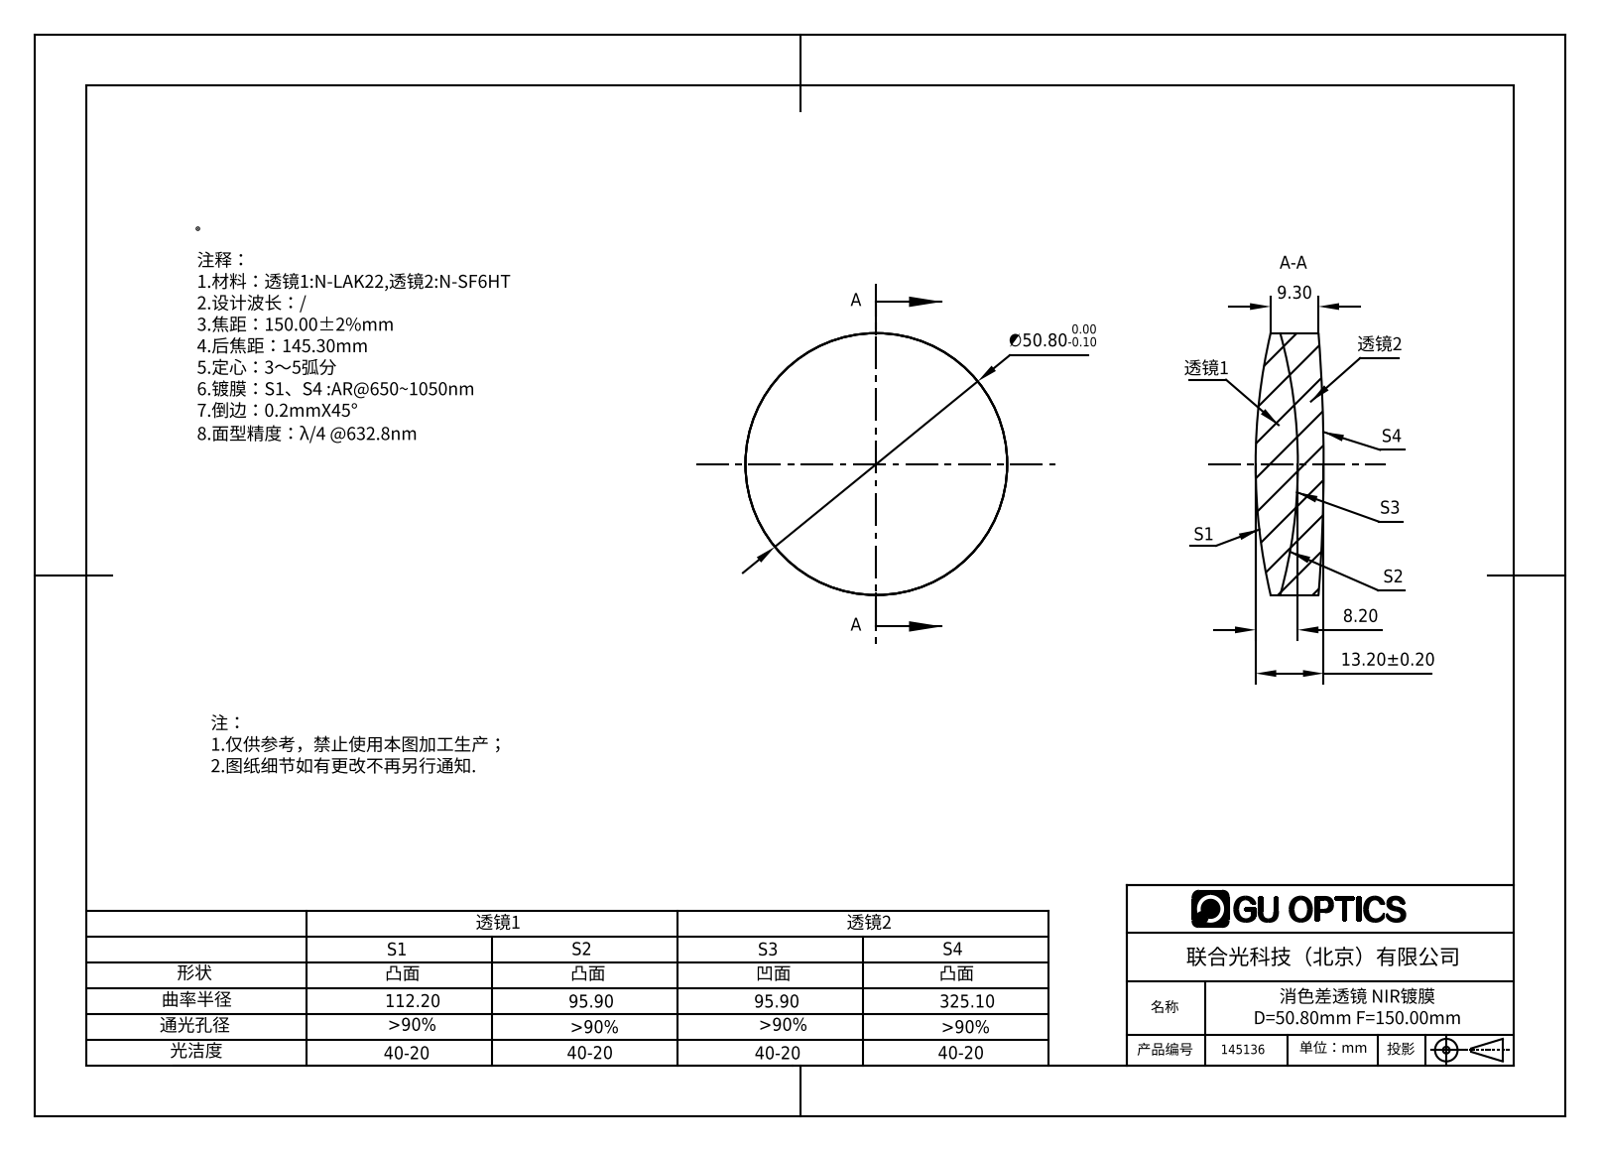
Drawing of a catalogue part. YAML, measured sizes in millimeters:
part_name: "145136"
step_written_by: "SolidWorks 2016 (AUTOMOTIVE_DESIGN)"
units: millimeters
bodies: {solids: 2, faces: 12, planar: 0, cylindrical: 4, other: 8}
overall_size: [50.8, 50.8, 13.2]
volume: 22809
surface_area: 9694
round_bosses_or_shafts:
  - {diameter: 50.8, count: 1}
